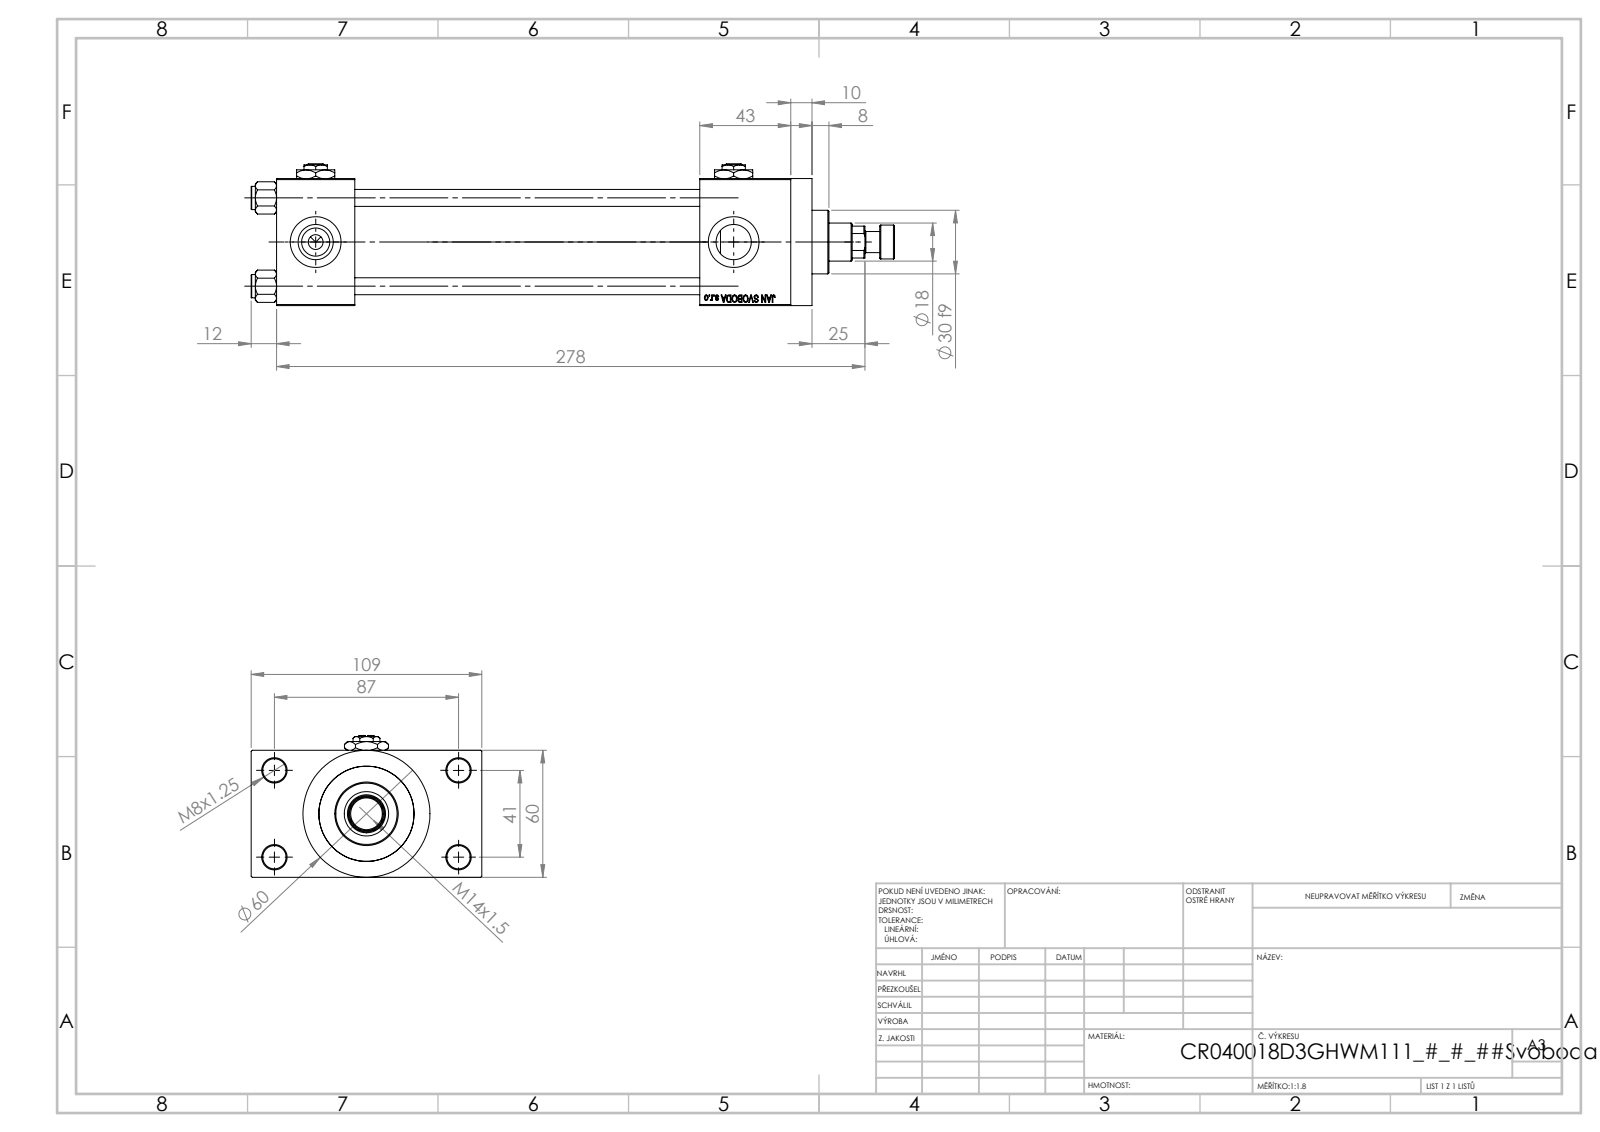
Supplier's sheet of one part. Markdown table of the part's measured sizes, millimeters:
| quantity | value |
| --- | --- |
| part name | V215_VC_A; V215CR_VCP_D; V215CR_ROD_END_W; V215CR_D_Body (+3 more) |
| STEP written by | SolidWorks 2019 (CONFIG_CONTROL_DESIGN) |
| units | millimeters |
| bodies | 14 solids, 1218 faces (549 planar, 103 cylindrical, 566 other) |
| overall size | 304 × 109 × 67 |
| volume | 602 677 mm³ |
| surface area | 171 030 mm² |
| round holes (diameter × count) | 8 × 4, 11 × 4, 16.66 × 4, 24 × 4, 7 × 3, 8.5 × 1, 18 × 1, 21 × 1, 31 × 1, 40 × 1, 45 × 1 |
| round bosses / shafts (diameter × count) | 11 × 4, 60 × 1, 46 × 1, 30 × 1, 16 × 1, 10 × 1 |
| partial cylindrical surfaces (radius × count) | 8.5 × 1 |
| main face-to-face distances | 60, 24.5, 163, 84.5, 37, 200, 43, 243, 206, 10 |
| hole center spacings | 22.65, 29.49, 41.7, 47.15, 48.09, 64.35, 76.49, 41 |
